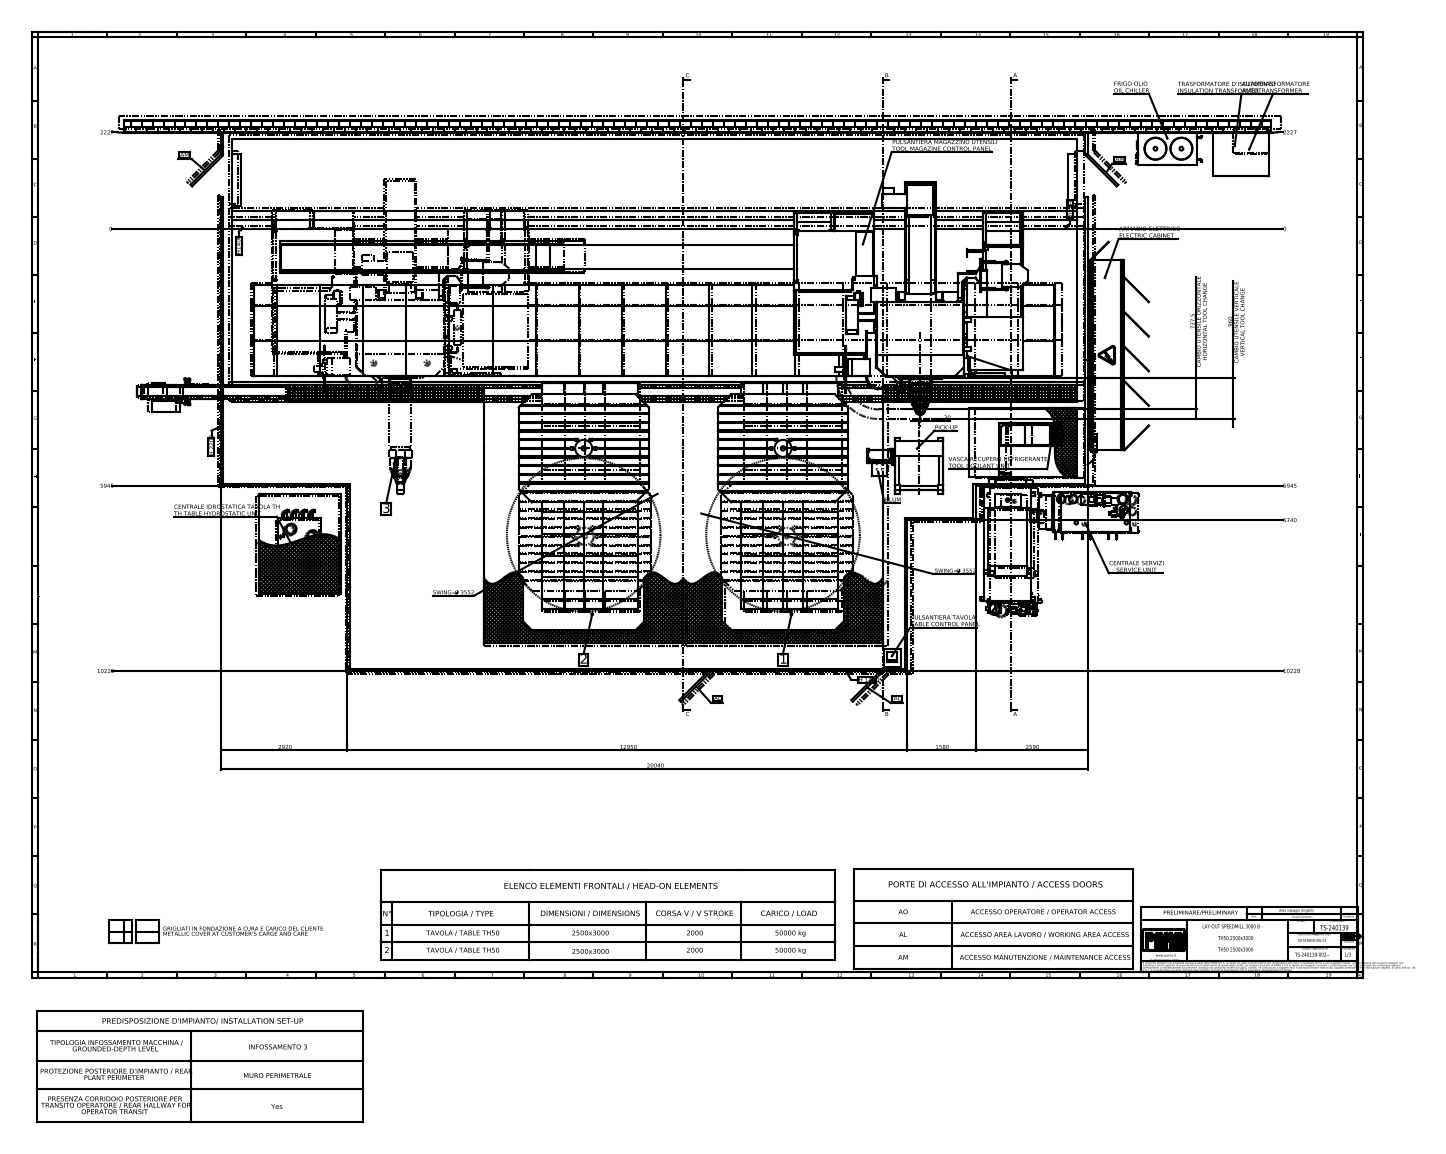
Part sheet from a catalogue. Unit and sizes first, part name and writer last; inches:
Units: inches
Overall size (bounding box): 1044.882 × 618.307 × 370.079
Round holes (diameter × count): ⌀1.378 ×181, ⌀2.74 ×83, ⌀0.551 ×8, ⌀0.315 ×6, ⌀1.26 ×6, ⌀0.472 ×4, ⌀1.969 ×3, ⌀3.937 ×3, ⌀0.402 ×2, ⌀0.748 ×2, ⌀3.15 ×2, ⌀3.189 ×2
Round bosses / shafts (diameter × count): ⌀2.362 ×12, ⌀3.15 ×10, ⌀1.181 ×8, ⌀7.874 ×6, ⌀1.378 ×6, ⌀9.843 ×5, ⌀5.906 ×5, ⌀1.969 ×4
Partial cylindrical surfaces — rounded edges, fillets, slot ends (radius × count): R0.197 ×113, R0.236 ×42, R0.591 ×37, R0.394 ×33, R0.787 ×32, R1.083 ×24, R1.378 ×24, R0.079 ×16
Main face-to-face distances: 78.74, 11.811, 1.969, 40.157, 38.583, 3.74, 43.898, 618.307, 606.496, 34.843
Hole centre spacings: 9.843, 19.685, 29.528, 39.37, 49.213, 59.055, 68.898, 78.74
Volume: 46 660 000 in³ · Surface area: 4 225 000 in²
Bodies: 470 solids, 7759 faces (5768 planar, 1543 cylindrical, 448 other)
Part name (STEP PRODUCT): S003182_Lato PO - Inf. 2-3; S003498_TM 80-130; S003332_LAMIERA; S003513_ISO 50 - RIPOSO (+8 more)
STEP written by: SolidWorks 2023 (AUTOMOTIVE_DESIGN)
